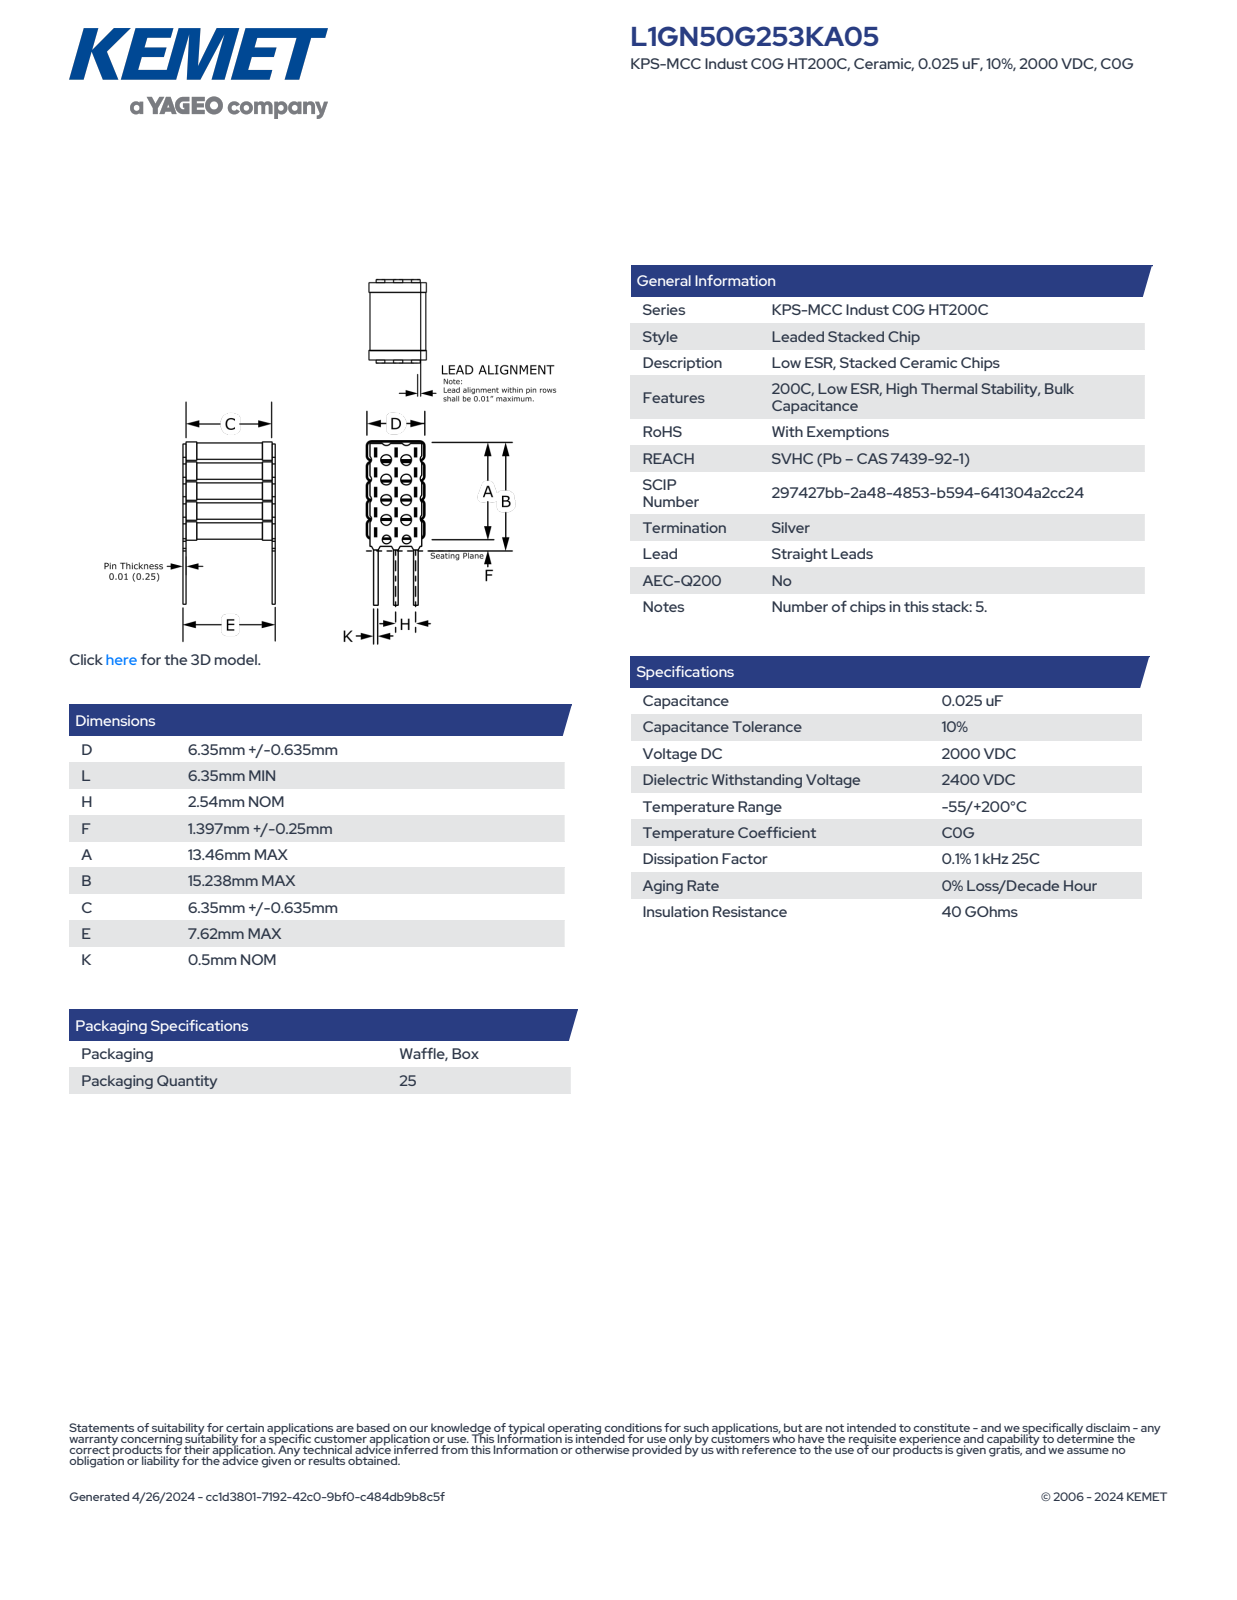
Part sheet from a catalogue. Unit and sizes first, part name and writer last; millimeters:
Units: millimetres
Overall size (bounding box): 15.49 × 10.04 × 6.99
Partial cylindrical surfaces — rounded edges, fillets, slot ends (radius × count): R0.2 ×2
Main face-to-face distances: 2.69, 5.38, 2.59, 2.79, 5.28, 8.07, 5.48, 6.89, 7.97, 2.49
Volume: 687 mm³ · Surface area: 957 mm²
Bodies: 4 solids, 223 faces (217 planar, 6 cylindrical, 0 other)
Part name (STEP PRODUCT): CCSS_LSN5_5_D6.99L6.35H2.54F1.647A13.46B15.238C6.985E7.62K0.5
STEP written by: SolidWorks 2014 (AUTOMOTIVE_DESIGN)
